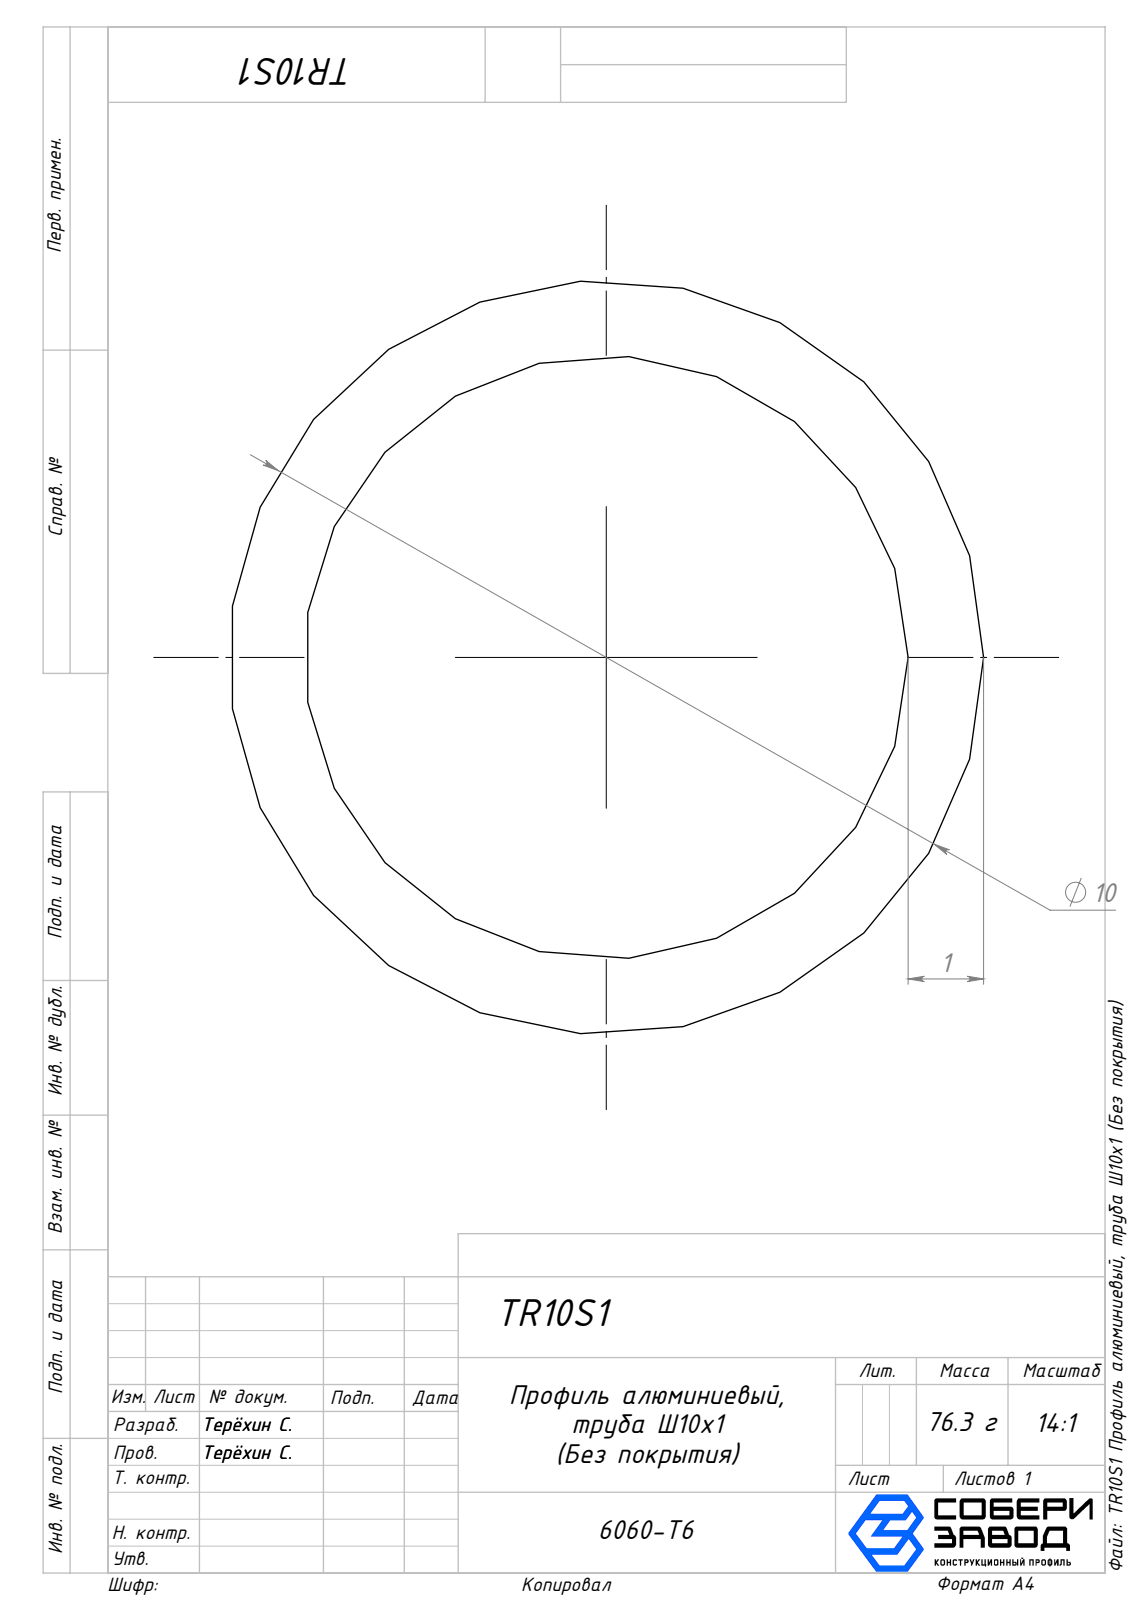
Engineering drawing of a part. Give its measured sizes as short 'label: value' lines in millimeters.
name: TR10S1 Профиль алюминиевый, труба Ø10х1 (Без покрытия)_00; Сборка9
written by: SolidWorks 2025 (AUTOMOTIVE_DESIGN)
unit: mm
bodies: 1 solid, 6 faces (2 planar, 4 cylindrical, 0 other)
size: 1000 × 10 × 10
volume: 28 274 mm³; area: 56 605 mm²
holes: 1× ⌀8
bosses: 1× ⌀10
face distances: 1000
